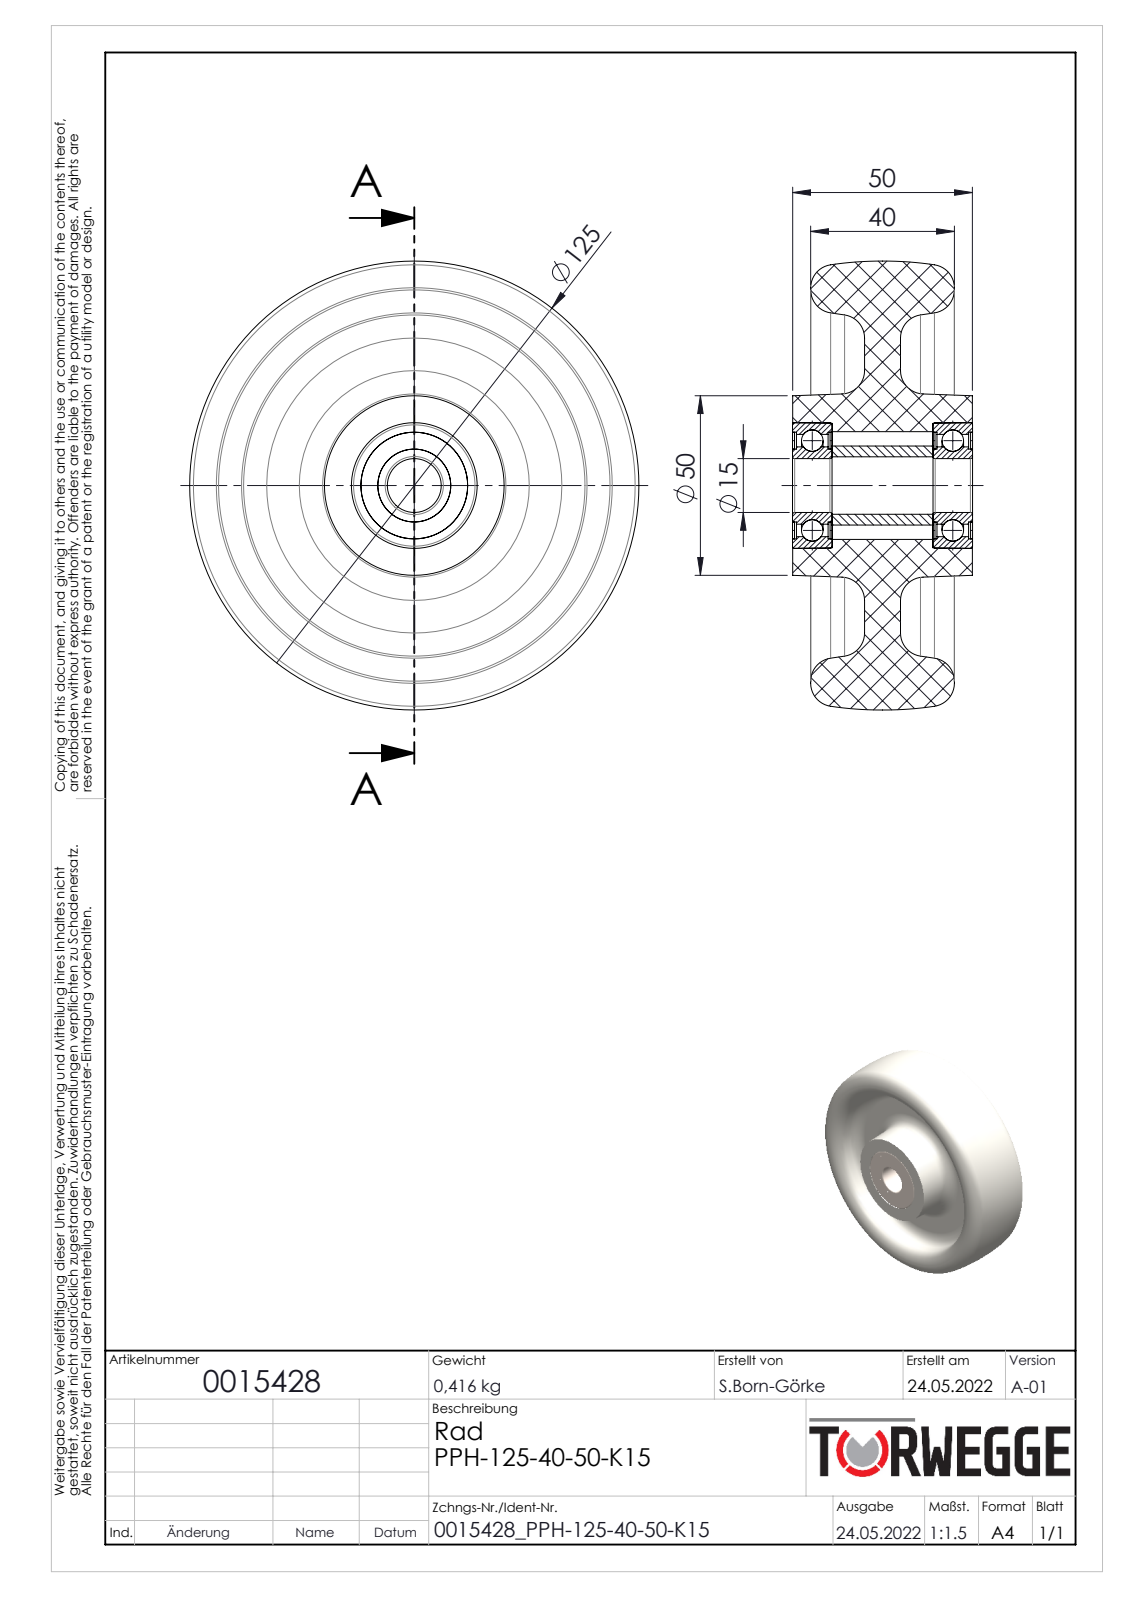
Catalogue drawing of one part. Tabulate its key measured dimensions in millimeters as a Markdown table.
| quantity | value |
| --- | --- |
| part name | 0015428 |
| STEP written by | SolidWorks 2020 (AUTOMOTIVE_DESIGN) |
| units | millimeters |
| bodies | 12 solids, 166 faces (32 planar, 62 cylindrical, 72 other) |
| overall size | 125 × 125 × 50.1 |
| volume | 323 156 mm³ |
| surface area | 70 599 mm² |
| round holes (diameter × count) | 15 × 1, 16 × 1, 20.3 × 1, 28.48 × 1, 29.7 × 1, 30 × 1 |
| round bosses / shafts (diameter × count) | 35 × 1, 22 × 1, 21.52 × 1 |
| main face-to-face distances | 39.1, 39.05, 10, 20, 30, 0.55, 11, 10.95, 9.05, 19.05 |
